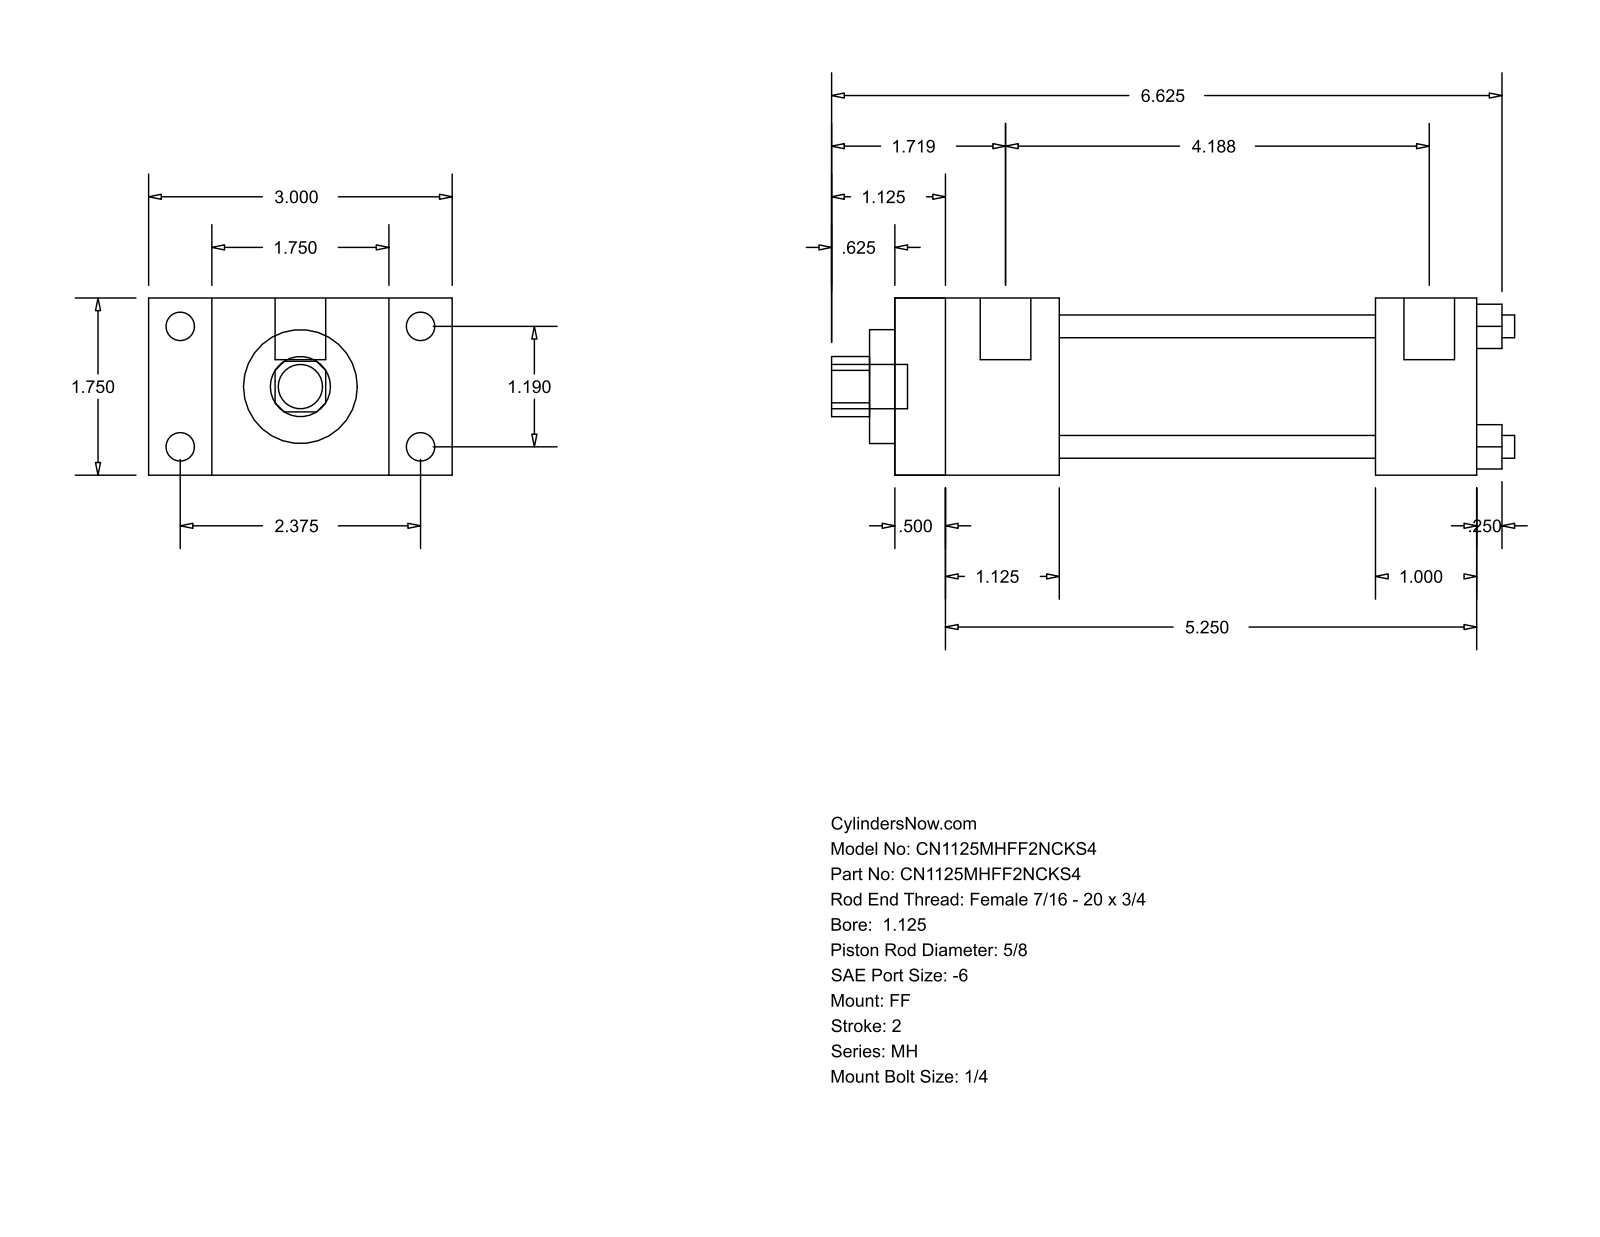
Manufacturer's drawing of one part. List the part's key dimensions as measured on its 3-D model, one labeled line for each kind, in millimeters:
Part name (STEP PRODUCT): MH_FF__0112_0.625
STEP written by: GSSL Pune (CONFIG_CONTROL_DESIGN)
Units: millimetres
Bodies: 0 solids, 92 faces (64 planar, 28 cylindrical, 0 other)
Overall size (bounding box): 171.45 × 76.2 × 44.45
Round holes (diameter × count): ⌀5.71 ×4, ⌀15.88 ×1, ⌀28.57 ×1, ⌀34.92 ×1
Round bosses / shafts (diameter × count): ⌀7.14 ×4, ⌀5.56 ×4, ⌀12.7 ×2, ⌀11.11 ×1
Partial cylindrical surfaces — rounded edges, fillets, slot ends (radius × count): R7.54 ×1
Main face-to-face distances: 44.46, 146.05, 15.87, 12.69, 133.36, 60.33, 28.58, 41.27, 120.65, 107.96
Hole centre spacings: 21.37, 30.22, 42.74
